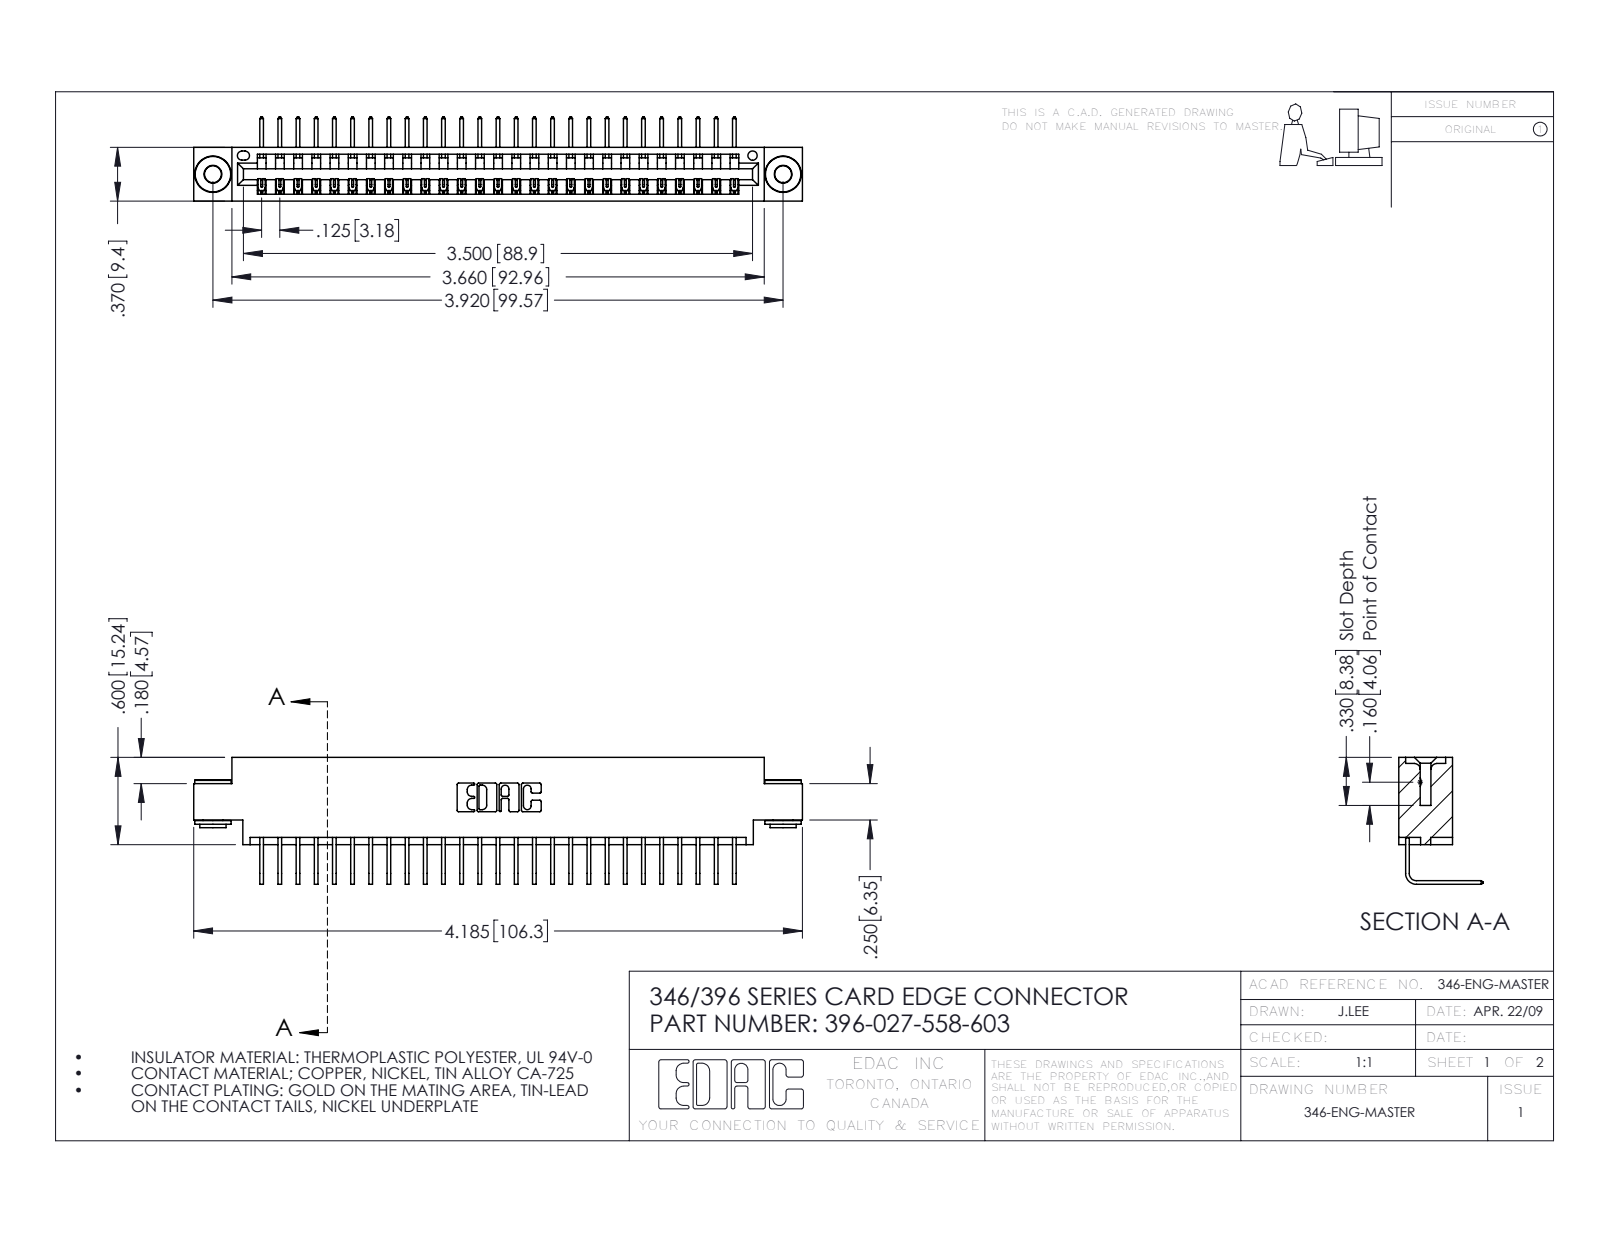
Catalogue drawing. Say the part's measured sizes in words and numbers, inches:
The part is named "396-027-558-603; 345-250-002_345-250-002-102; 346 Part_0.170 Offset - 0.156 Dia-TH; 345-292-001_558 Tail - 2". Its 3-D file was written by "SolidWorks 2016 (CONFIG_CONTROL_DESIGN)". It is 30 solids with 1784 faces: 1224 planar, 552 cylindrical and 8 other. Overall it measures 4.185 by 0.873 by 0.58 inches. Its volume is 0.612 cubic inches and its surface area 20.59 square inches. Round holes: 2 of diameter 0.116, 2 of diameter 0.156, 1 of diameter 0.064. Round bosses or shafts: 2 of diameter 0.25, 2 of diameter 0.18, 2 of diameter 0.136. Partial cylindrical surfaces (rounded edges, fillets, slot ends): 54 of radius 0.006, 22 of radius 0.01, 6 of radius 0.007, 6 of radius 0.031, 3 of radius 0.026, 2 of radius 0.031, 2 of radius 0.04, 1 of radius 0.014. The main face-to-face distances are 0.322, 0.048, 0.37, 0.25, 0.025, 0.298, 0.072, 0.148, 0.222, 0.1. The hole center spacings are 0.246, 3.712, 3.92.
